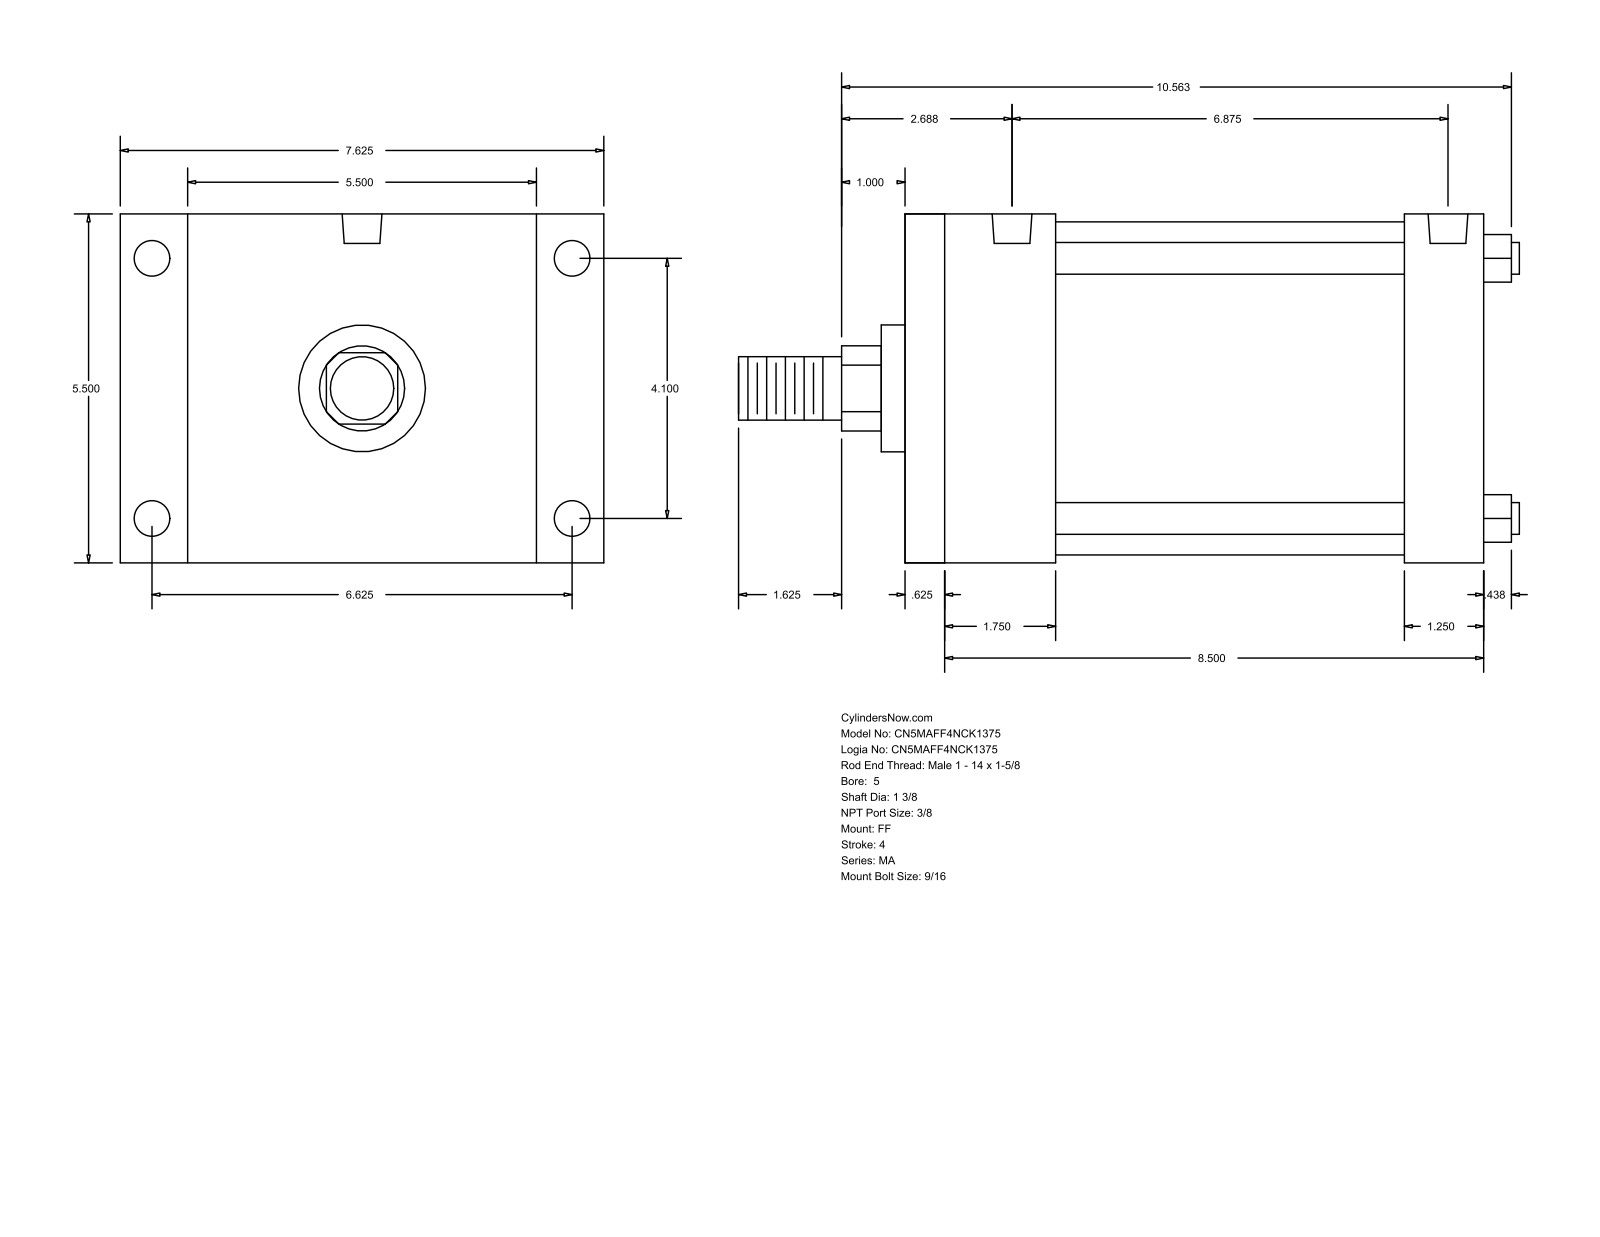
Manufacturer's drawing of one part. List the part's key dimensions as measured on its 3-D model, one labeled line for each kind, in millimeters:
Part name (STEP PRODUCT): MA_FF__0500_1.375
STEP written by: GSSL Pune (CONFIG_CONTROL_DESIGN)
Units: millimetres
Bodies: 0 solids, 92 faces (64 planar, 28 cylindrical, 0 other)
Overall size (bounding box): 312.74 × 193.68 × 139.7
Round holes (diameter × count): ⌀11.11 ×4, ⌀14.29 ×4, ⌀15.93 ×2
Round bosses / shafts (diameter × count): ⌀12.7 ×4, ⌀133.35 ×1, ⌀50.8 ×1, ⌀34.92 ×1, ⌀25.4 ×1
Partial cylindrical surfaces — rounded edges, fillets, slot ends (radius × count): R17.06 ×1
Main face-to-face distances: 139.7, 231.78, 15.87, 215.91, 200.03, 184.16, 31.75, 60.32, 44.45, 139.71
Hole centre spacings: 4.77, 104.14, 165.09, 168.28, 169.86, 197.9, 174.63
